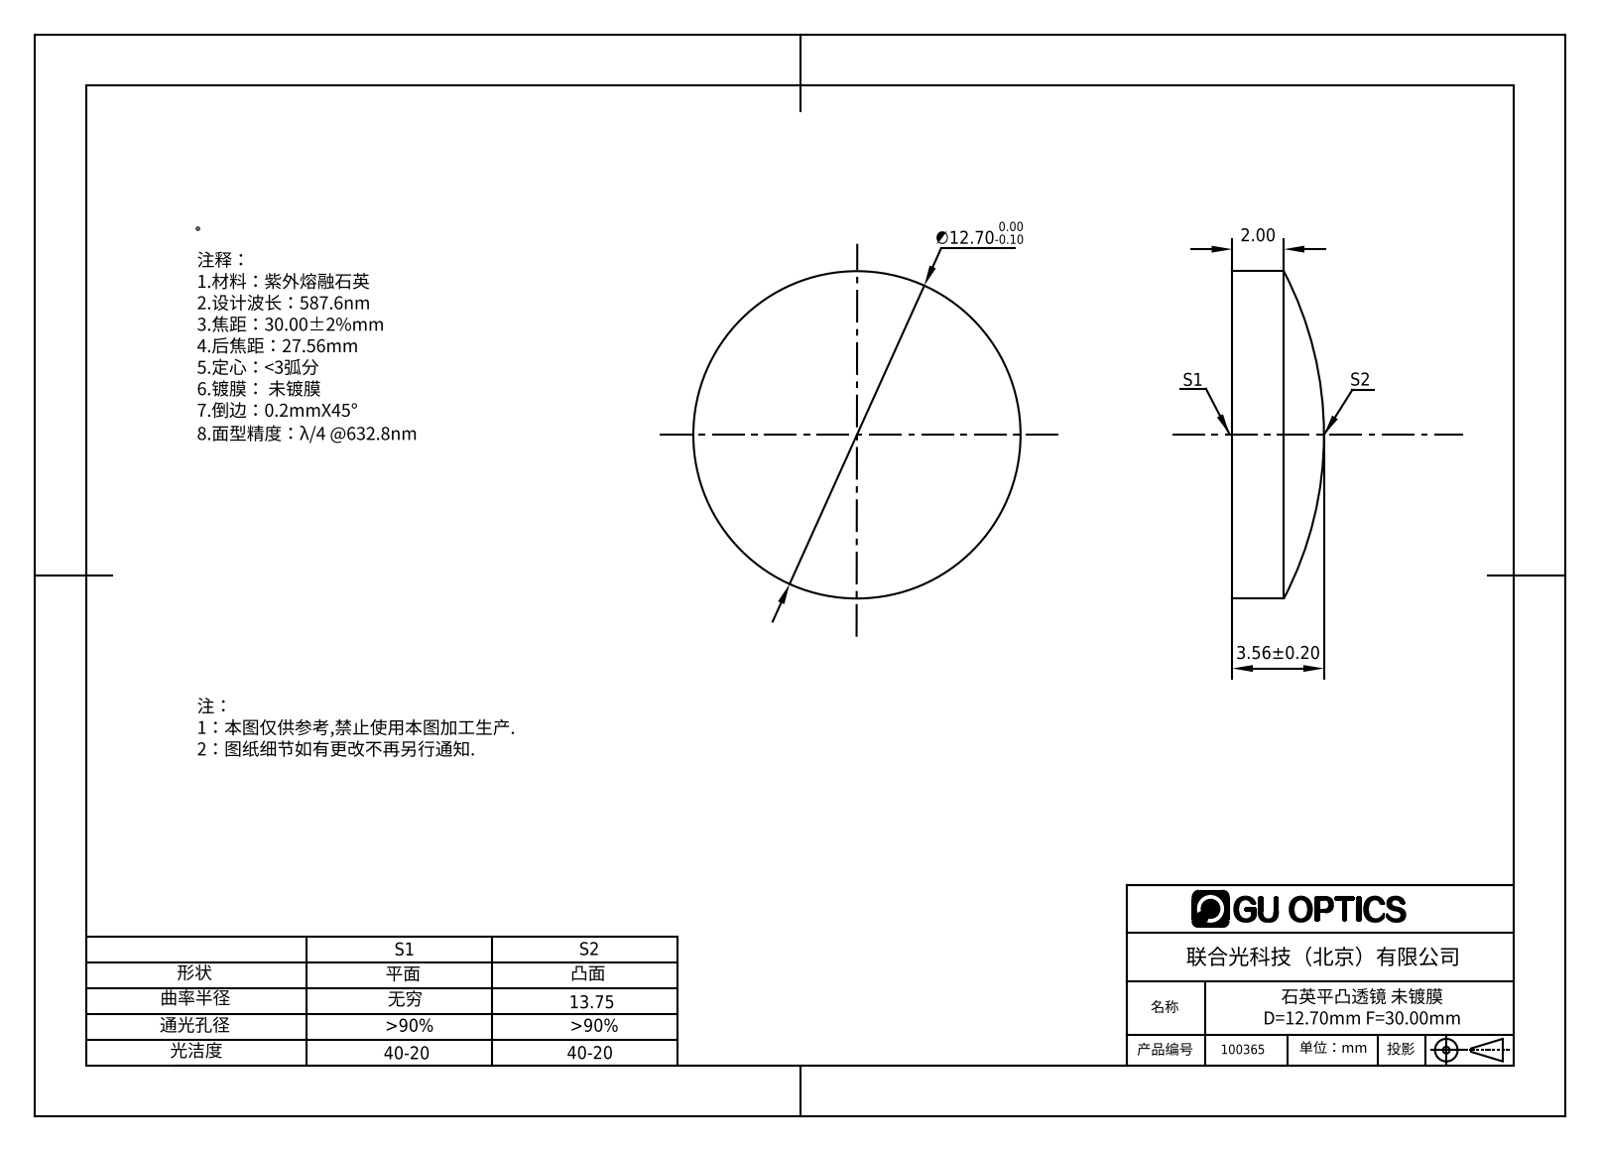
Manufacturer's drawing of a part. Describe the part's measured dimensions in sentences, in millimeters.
The part is named "100366". Its 3-D file was written by "SolidWorks 2016 (AUTOMOTIVE_DESIGN)". It is 1 solid with 5 faces: 1 planar, 2 cylindrical and 2 other. Overall it measures 12.7 by 12.7 by 3.56 millimeters. Its volume is 354 cubic millimeters and its surface area 341 square millimeters. Round bosses or shafts: 1 of diameter 12.7.
